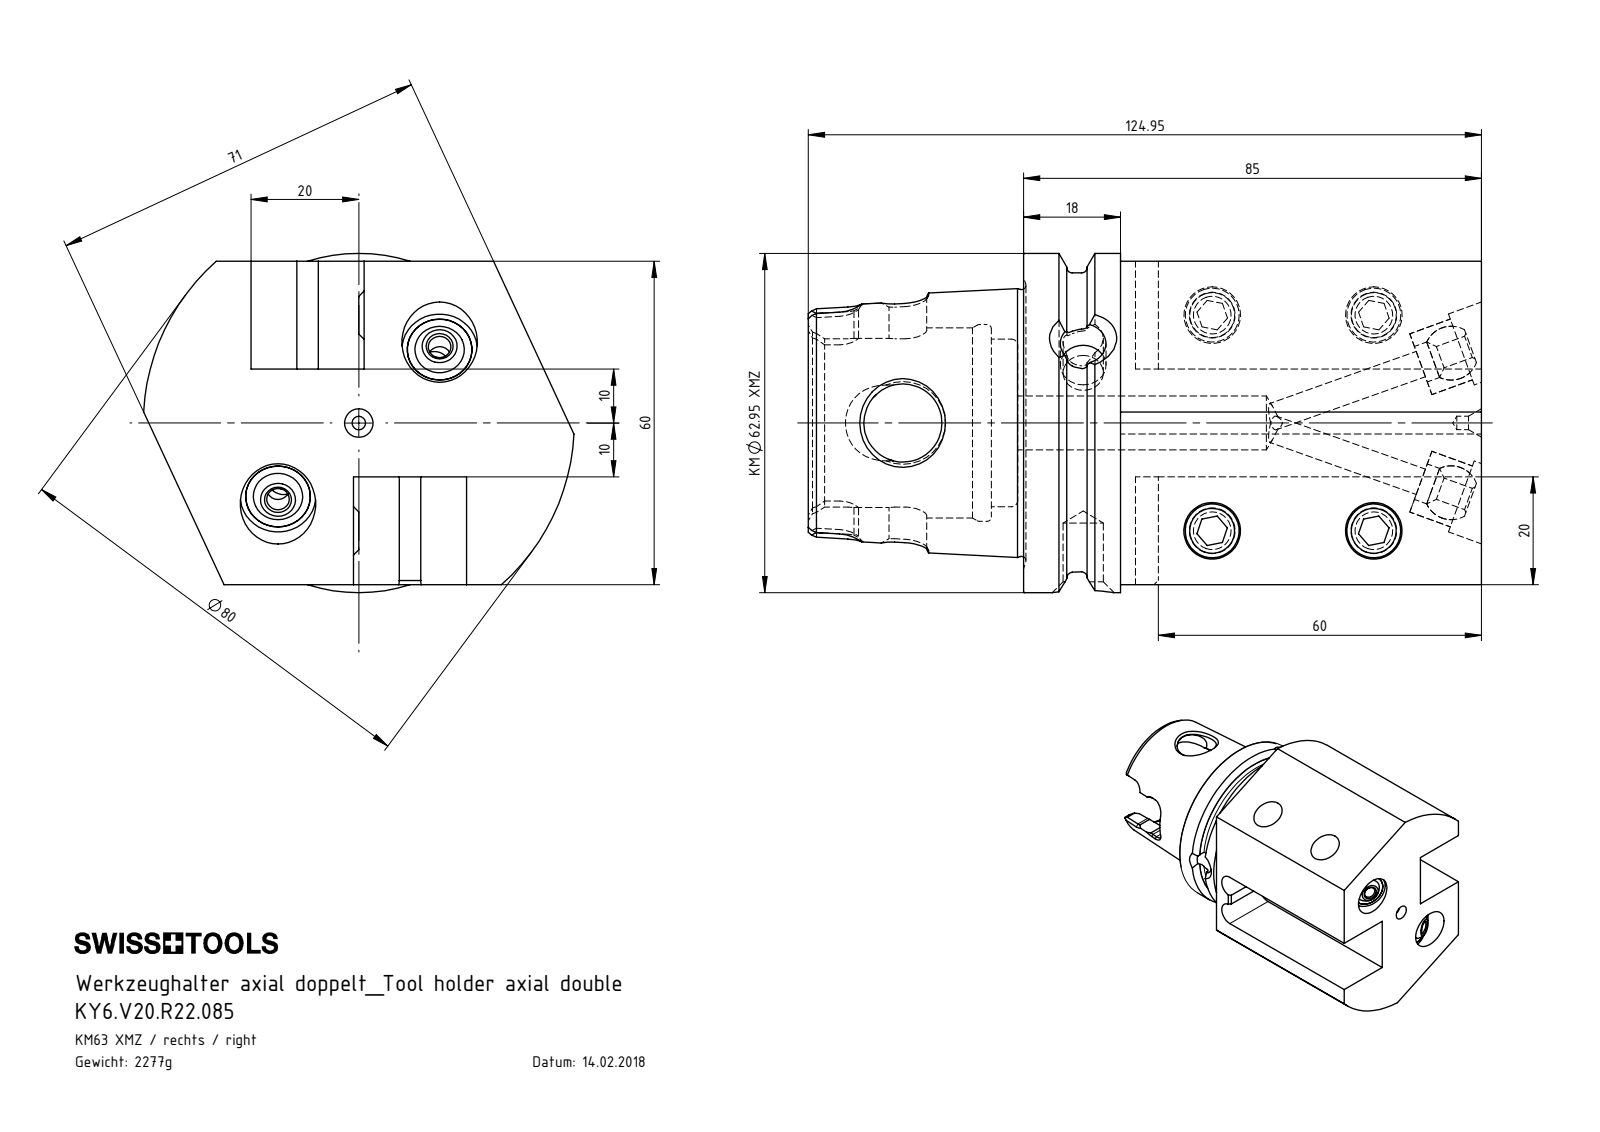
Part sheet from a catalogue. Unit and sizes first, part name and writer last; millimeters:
Units: millimetres
Overall size (bounding box): 124.95 × 79.89 × 62.95
Round holes (diameter × count): ⌀8.5 ×4, ⌀10.5 ×4, ⌀4.2 ×2, ⌀5 ×2, ⌀7 ×2, ⌀7.47 ×2, ⌀12 ×2, ⌀14 ×2, ⌀2.5 ×1, ⌀8.48 ×1, ⌀10 ×1, ⌀14.5 ×1
Round bosses / shafts (diameter × count): ⌀10 ×4, ⌀12 ×2, ⌀62.95 ×1, ⌀55.7 ×1
Partial cylindrical surfaces — rounded edges, fillets, slot ends (radius × count): R4 ×6, R4.25 ×4, R7.04 ×2, R40 ×1
Main face-to-face distances: 20, 40, 60, 70.65, 19, 21, 2, 67, 18, 85
Hole centre spacings: 30, 40, 50, 60.78, 89.66
Volume: 290 581 mm³ · Surface area: 54 395 mm²
Bodies: 9 solids, 320 faces (93 planar, 97 cylindrical, 130 other)
Part name (STEP PRODUCT): KU1-U12.001.010_1; KU1-U12.001.010; KY6-V20.L22.085_A; ISO 4026 - M10 x 20_PreviewCfg (+2 more)
STEP written by: SolidWorks 2017 (CONFIG_CONTROL_DESIGN)
